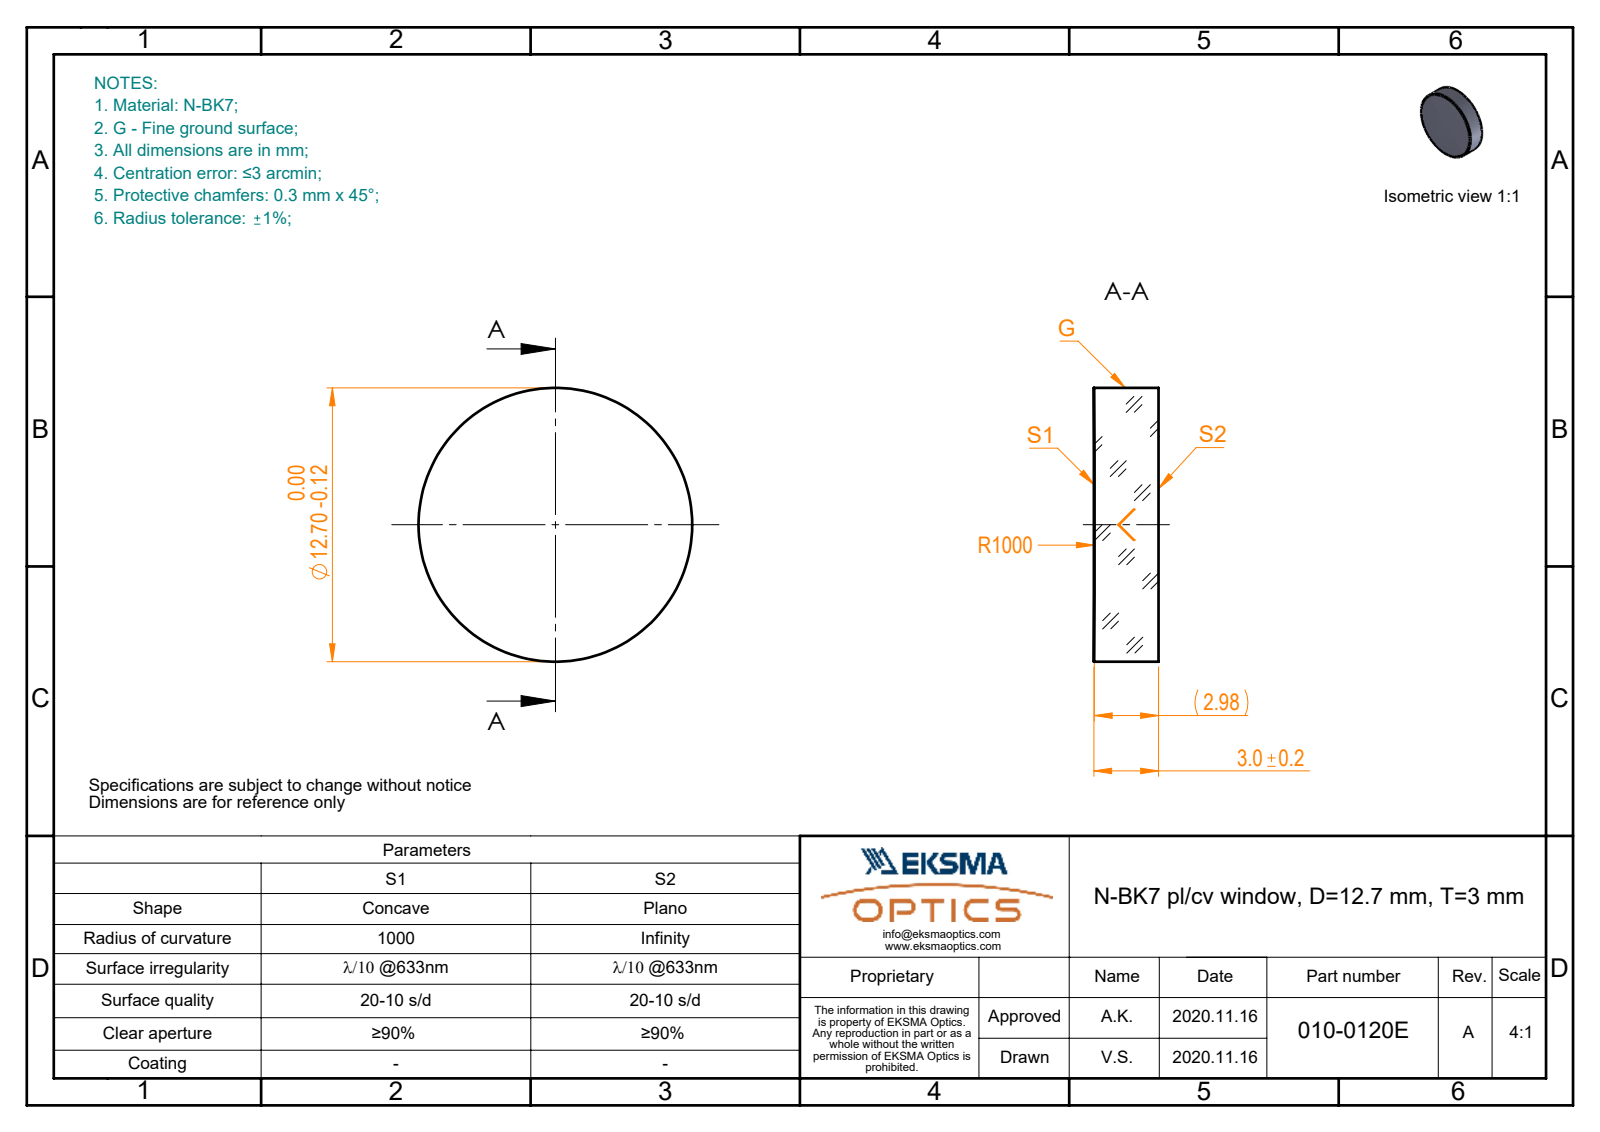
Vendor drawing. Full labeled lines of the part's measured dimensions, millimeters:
Part name (STEP PRODUCT): 010-0120E_N-BK7_PCV_window
STEP written by: SolidWorks 2019 (CONFIG_CONTROL_DESIGN)
Units: millimetres
Bodies: 1 solid, 5 faces (1 planar, 2 cylindrical, 2 other)
Overall size (bounding box): 12.7 × 12.7 × 3
Volume: 379 mm³ · Surface area: 373 mm²
Round bosses / shafts (diameter × count): ⌀12.7 ×1
